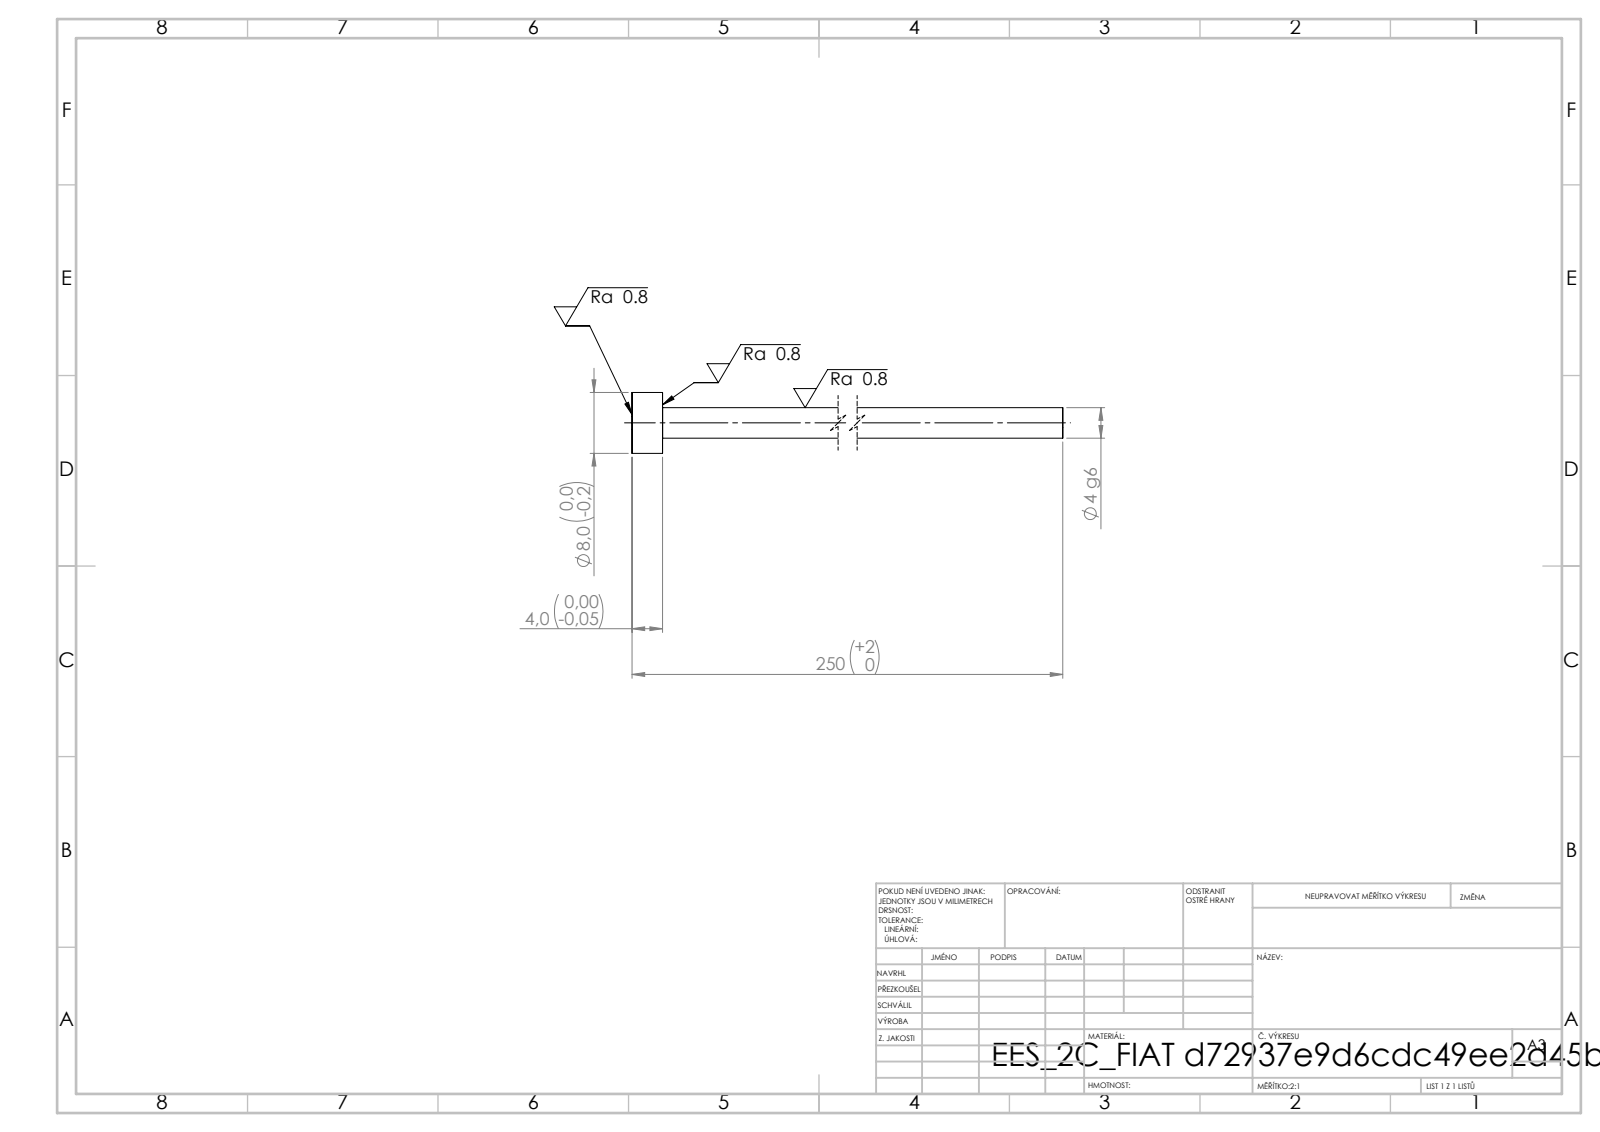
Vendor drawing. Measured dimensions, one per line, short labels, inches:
written by: SolidWorks 2019 (CONFIG_CONTROL_DESIGN)
unit: in
bodies: 1 solid, 7 faces (3 planar, 4 cylindrical, 0 other)
size: 9.843 × 0.315 × 0.315
volume: 0.201 in³; area: 5.103 in²
bosses: 1× ⌀0.315, 1× ⌀0.157
face distances: 0.157, 9.843, 9.685
